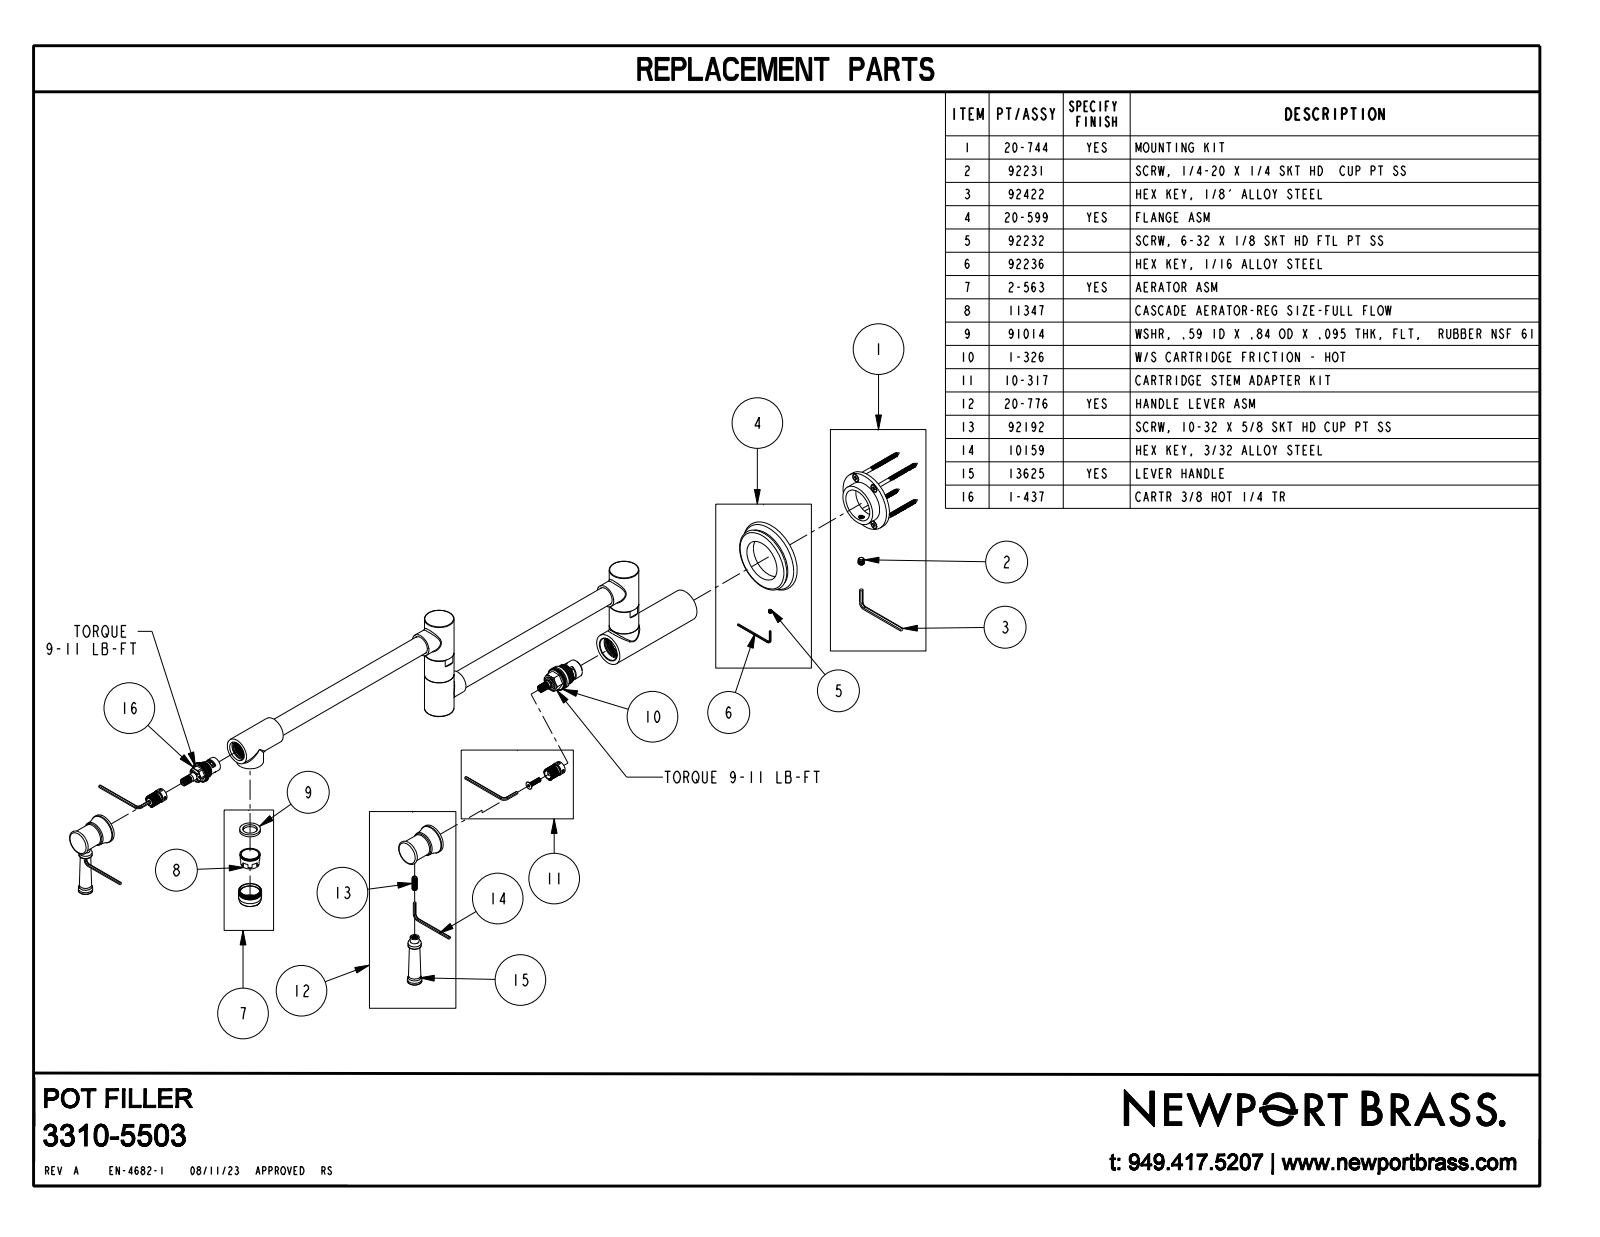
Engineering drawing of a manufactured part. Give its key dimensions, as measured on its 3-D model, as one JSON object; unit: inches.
{"part_name": "3310-5503", "step_written_by": "CREO PARAMETRIC BY PTC INC, 2018400 (CONFIG_CONTROL_DESIGN)", "units": "inches", "bodies": {"solids": 1, "faces": 233, "planar": 65, "cylindrical": 78, "other": 90}, "overall_size": [27.153, 8.946, 3], "volume_in3": 31.06, "surface_area_in2": 140.6, "round_holes": [[0.375, 2], [0.76, 2], [0.95, 2], [0.665, 1], [0.792, 1]], "round_bosses_or_shafts": [[0.94, 4], [1.2, 2], [1.19, 2], [1.1, 2], [1.03, 2], [0.9, 2], [0.75, 2], [0.58, 2]], "partial_cylinders_radius": [[0.115, 1]], "face_to_face_distances": [0.57, 2.86, 1.576, 4.437, 21.248, 1.676, 0.02, 1.696, 5.905, 27.153], "hole_center_spacings": [1.824, 1.967, 2.86, 8.604, 10.57, 10.82, 12.644, 19.424]}
